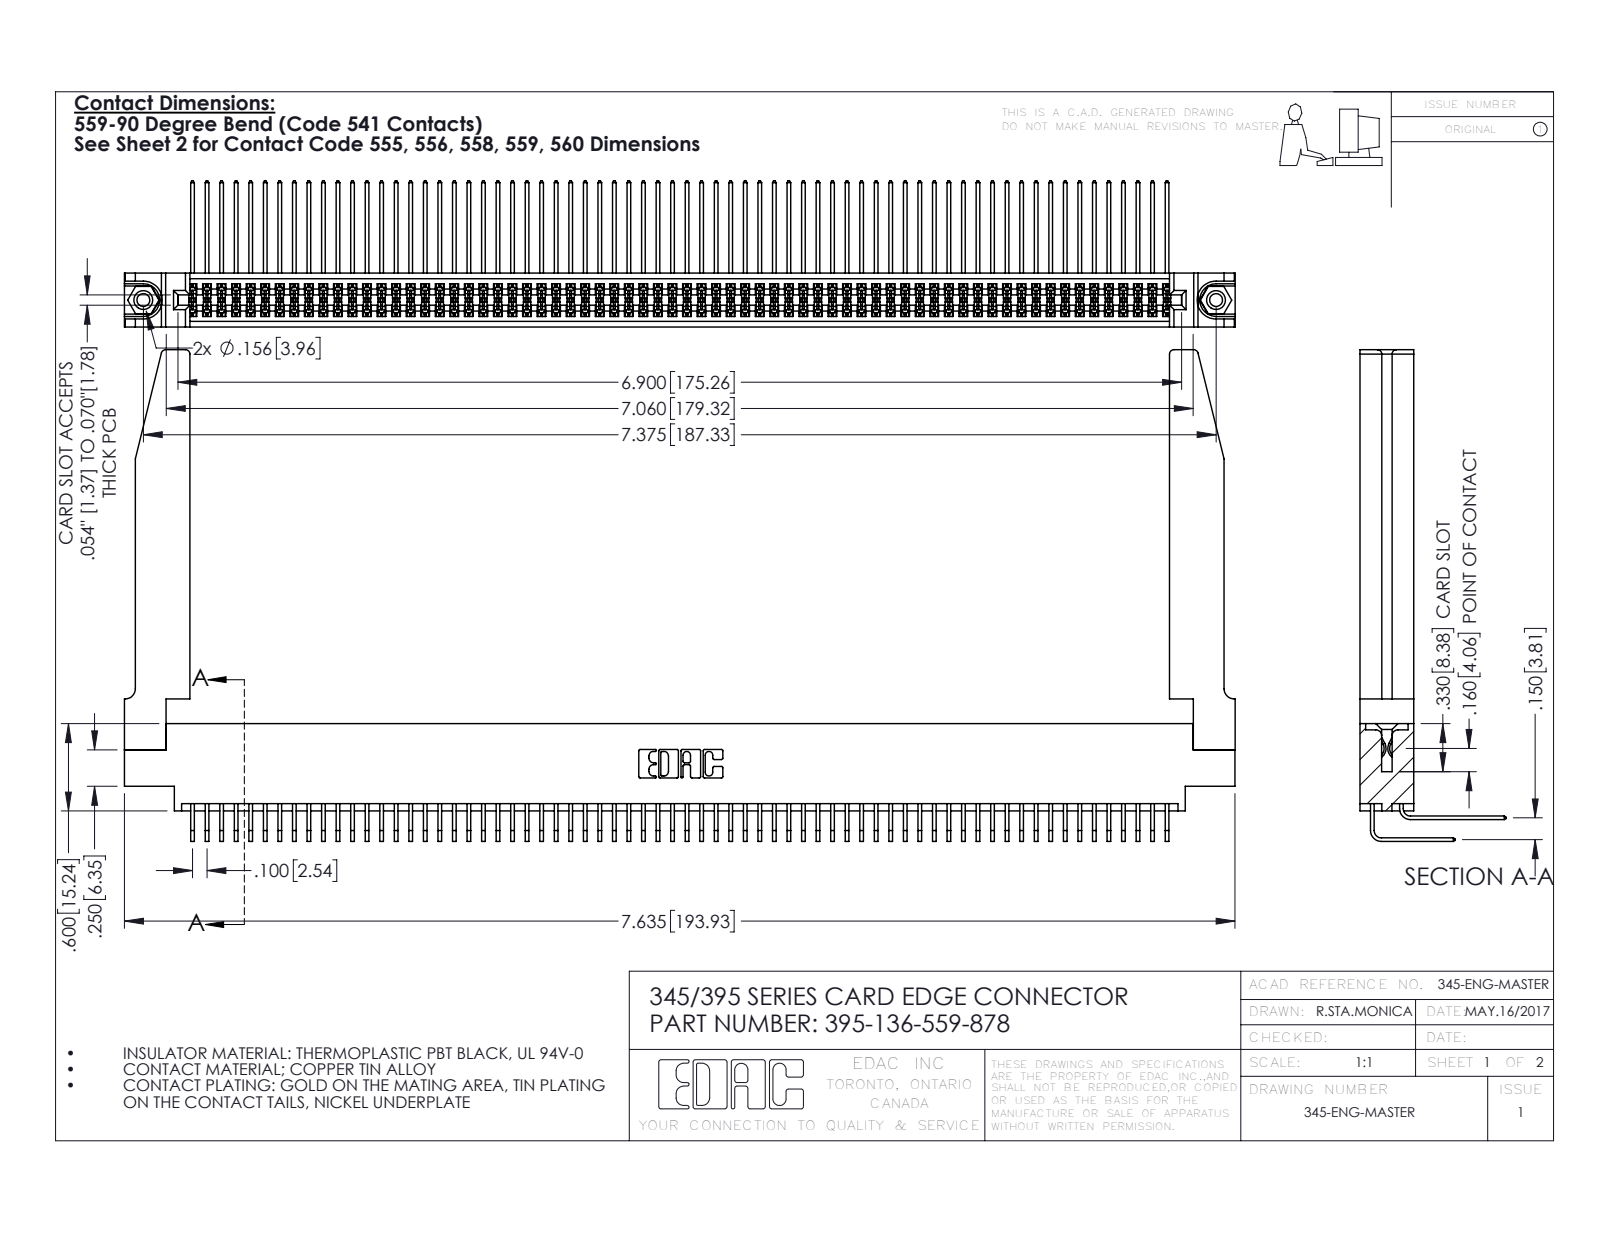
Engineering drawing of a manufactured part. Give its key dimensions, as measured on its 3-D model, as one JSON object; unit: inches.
{"part_name": "345-292-001_558 559 Tail - 1; 345 Part_0.170 Offset - 0.156 Dia-TH; 345-220-078_345-220-078; 345-292-001_559 Tail - 2 (+2 more)", "step_written_by": "SolidWorks 2016 (CONFIG_CONTROL_DESIGN)", "units": "inches", "bodies": {"solids": 141, "faces": 7436, "planar": 4986, "cylindrical": 2398, "other": 52}, "overall_size": [7.636, 3.379, 1.005], "volume_in3": 1.68, "surface_area_in2": 62.58, "round_holes": [[0.089, 2], [0.125, 2], [0.156, 2], [0.064, 1]], "round_bosses_or_shafts": [[0.155, 2]], "partial_cylinders_radius": [[0.006, 272], [0.01, 22], [0.03, 8], [0.007, 6], [0.031, 6], [0.026, 3], [0.014, 2], [0.019, 2]], "face_to_face_distances": [0.072, 0.298, 0.37, 0.098, 0.272, 0.025, 0.2, 0.225, 0.175, 0.15], "hole_center_spacings": [0.27, 7.139, 7.375]}
